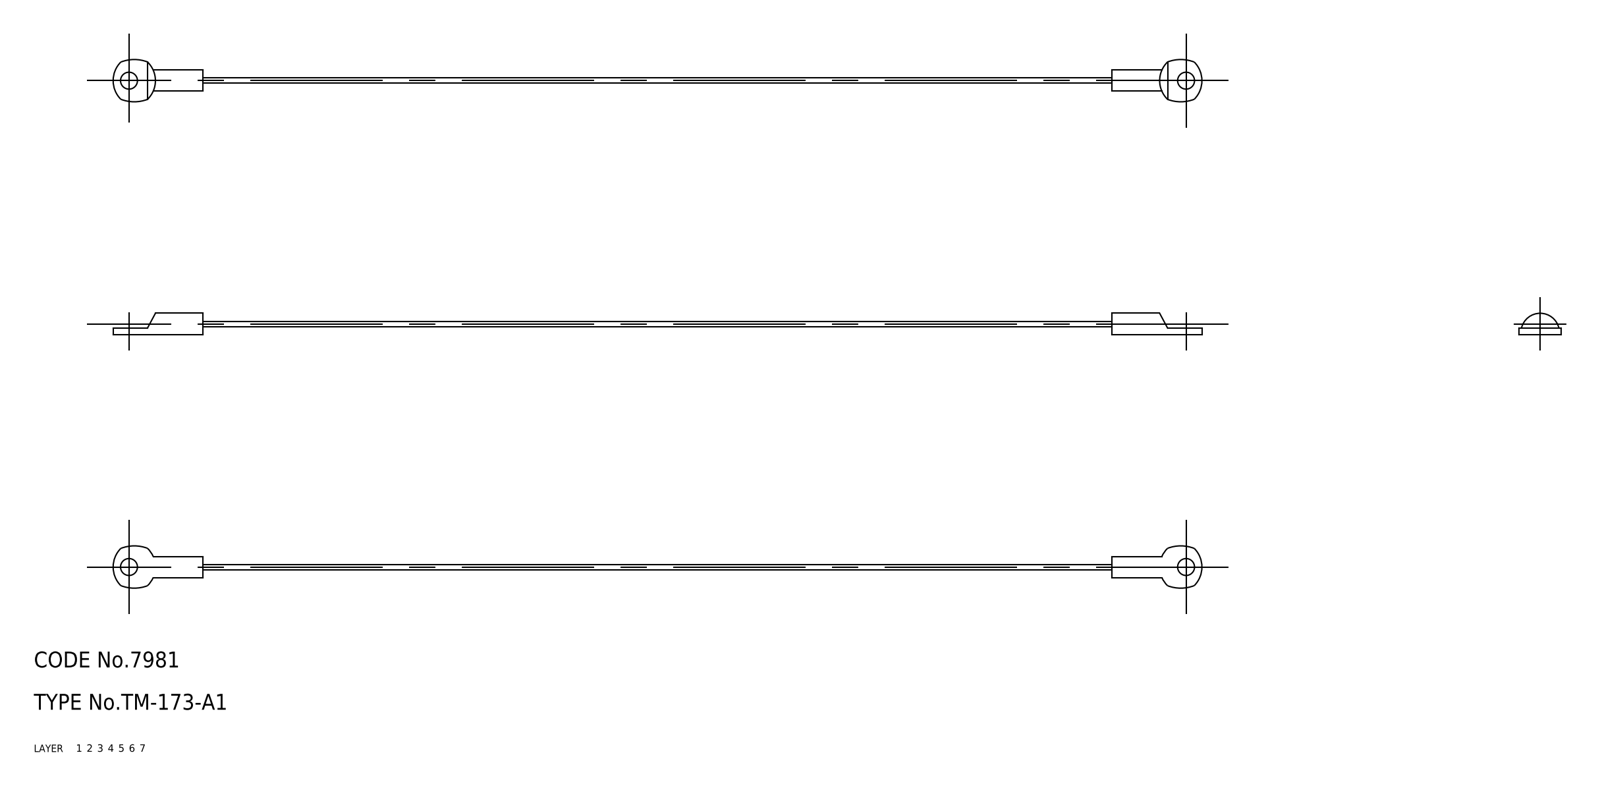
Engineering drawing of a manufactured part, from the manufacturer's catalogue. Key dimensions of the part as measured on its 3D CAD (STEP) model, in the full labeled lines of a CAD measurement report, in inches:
Part name (STEP PRODUCT): terminal; wire; TM_173_A1_28231_36
STEP written by: CADfix (AUTOMOTIVE_DESIGN)
Units: inches
Bodies: 3 solids, 56 faces (0 planar, 0 cylindrical, 56 other)
Overall size (bounding box): 8.11 × 0.315 × 0.157
Volume: 0.029 in³ · Surface area: 1.845 in²
